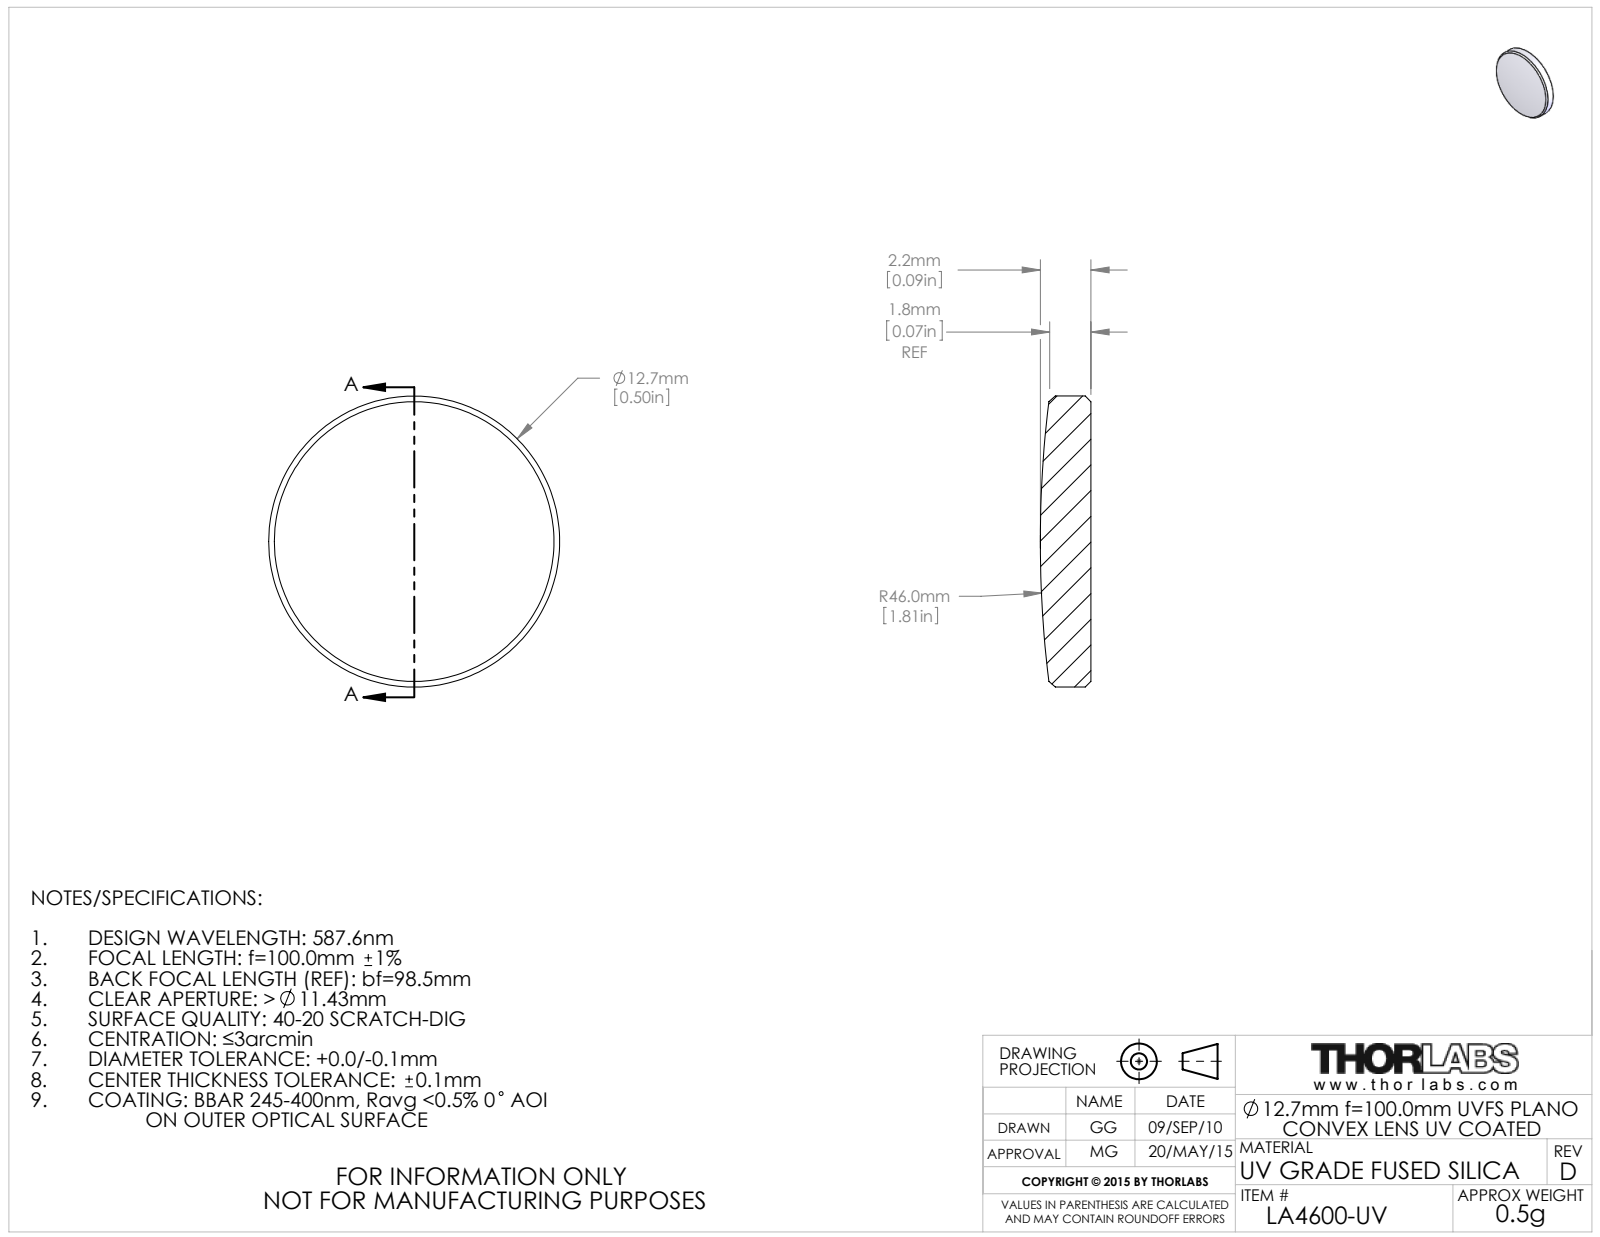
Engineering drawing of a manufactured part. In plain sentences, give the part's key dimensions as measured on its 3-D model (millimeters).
The part is named "4277-E0W". Its 3-D file was written by "SolidWorks 2014 (CONFIG_CONTROL_DESIGN)". It is 1 solid with 9 faces: 1 planar, 2 cylindrical and 6 other. Overall it measures 12.7 by 12.7 by 2.2 millimeters. Its volume is 252 cubic millimeters and its surface area 315 square millimeters. Round bosses or shafts: 1 of diameter 12.7.
